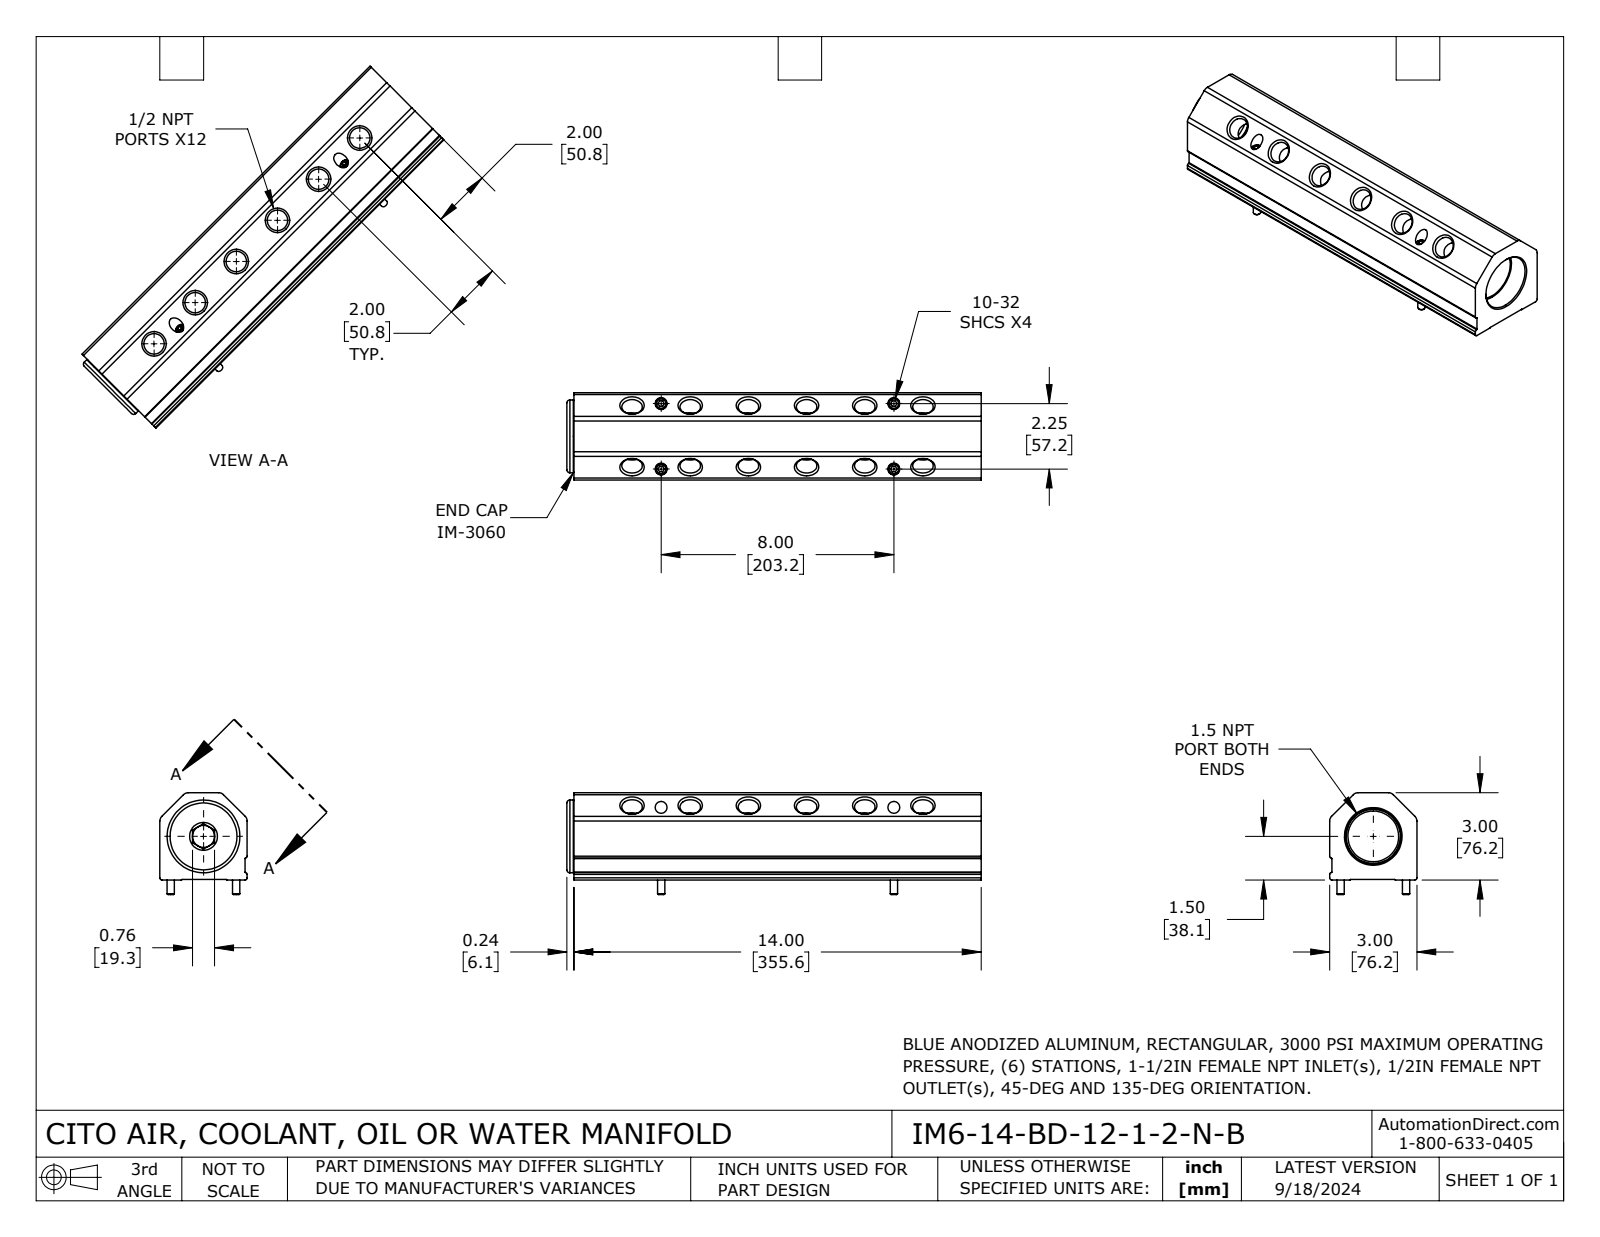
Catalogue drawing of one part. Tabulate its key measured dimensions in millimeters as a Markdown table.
| quantity | value |
| --- | --- |
| part name | IM6-14-BD-12-1-2-N-B |
| STEP written by | SolidWorks 2023 (CONFIG_CONTROL_DESIGN) |
| units | millimeters |
| bodies | 6 solids, 226 faces (76 planar, 82 cylindrical, 68 other) |
| overall size | 361.7 × 88.9 × 76.2 |
| volume | 1 297 000 mm³ |
| surface area | 183 900 mm² |
| round holes (diameter × count) | 17.9 × 12, 6.8 × 4, 10.3 × 4, 19.3 × 1, 44.3 × 1, 57.5 × 1 |
| round bosses / shafts (diameter × count) | 9.5 × 4, 6.4 × 4, 63.5 × 1, 50.4 × 1, 44.7 × 1 |
| partial cylindrical surfaces (radius × count) | 0.5 × 6, 5.7 × 4, 1.6 × 2, 1.9 × 2 |
| main face-to-face distances | 76.2, 0.5, 75.7, 1.9, 74.3, 355.6, 6.1, 361.7, 19.4, 13.3 |
| hole center spacings | 50.8, 101.6, 152.4, 203.2, 57.2, 211.1, 254 |
